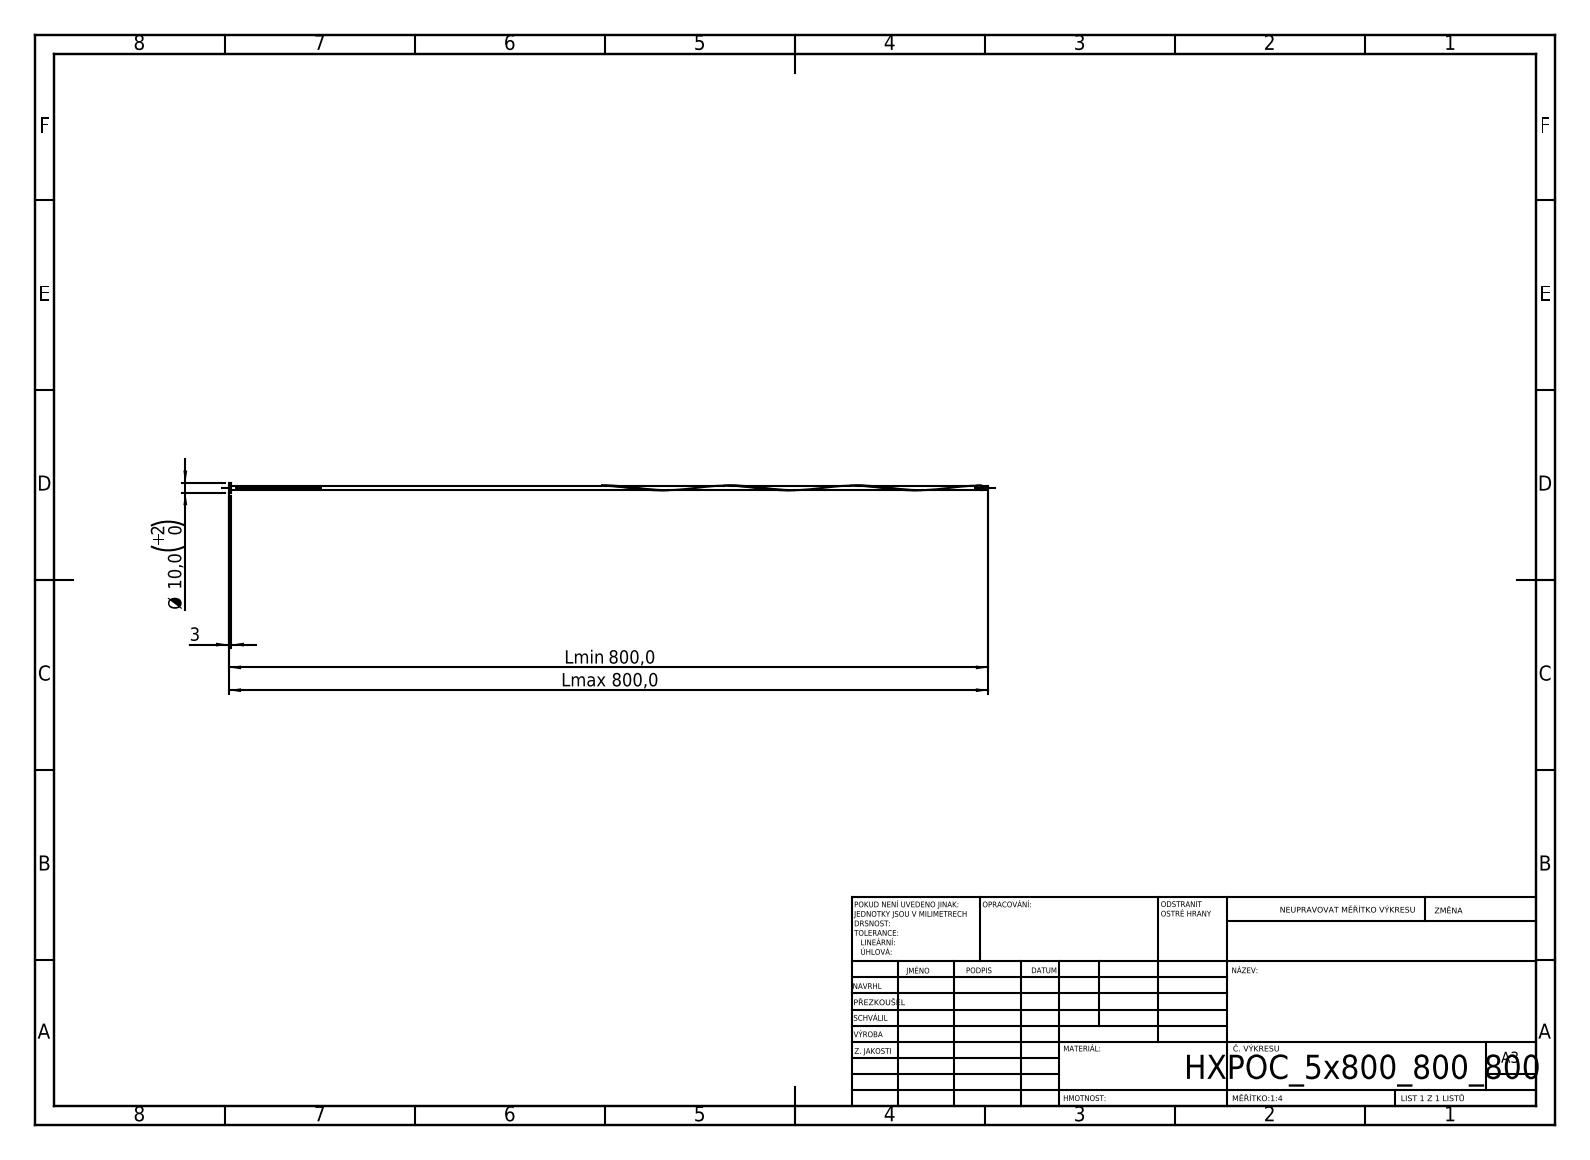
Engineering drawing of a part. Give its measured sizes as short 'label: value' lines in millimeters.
written by: SolidWorks 2019 (CONFIG_CONTROL_DESIGN)
unit: mm
bodies: 1 solid, 16 faces (6 planar, 9 cylindrical, 1 other)
size: 800 × 10 × 10
volume: 19 217 mm³; area: 17 159 mm²
bosses: 1× ⌀10, 1× ⌀5, 1× ⌀4
face distances: 3, 800, 797, 793.27, 790.27, 6.73, 792.27, 789.27, 1, 7.73
